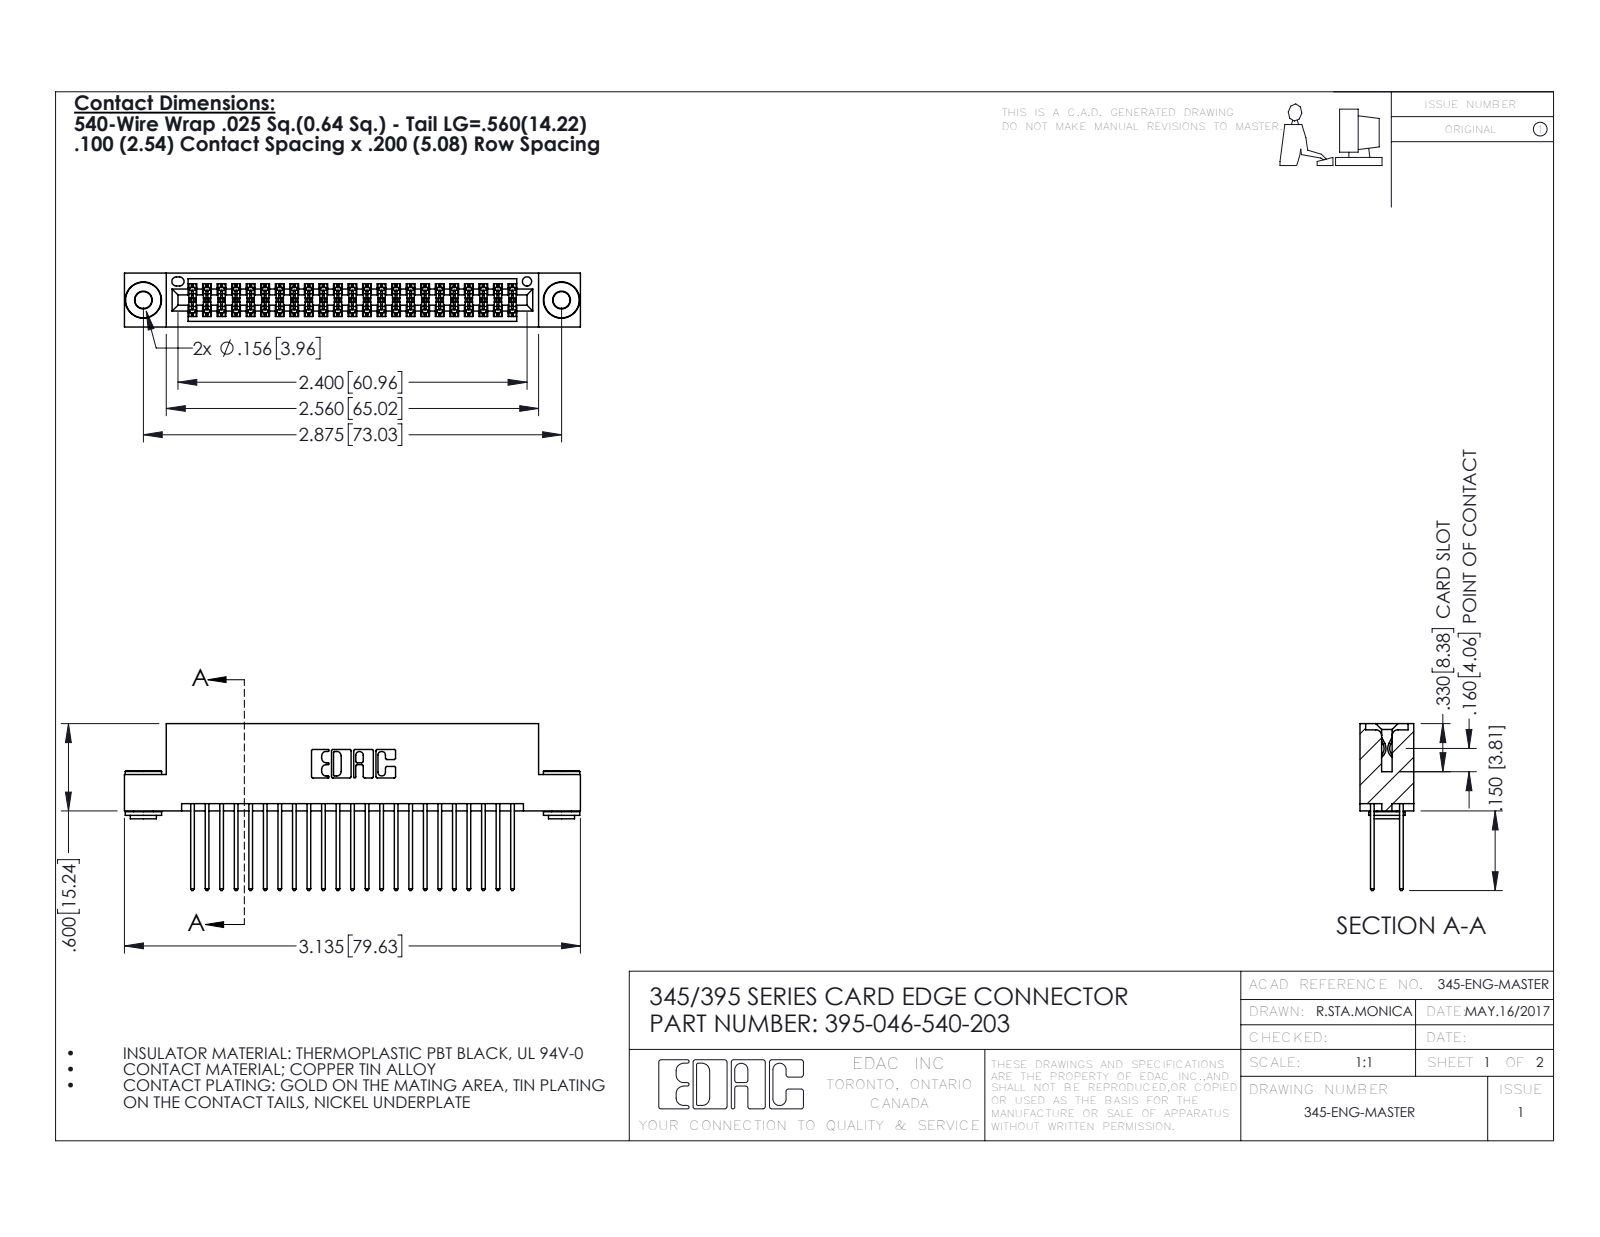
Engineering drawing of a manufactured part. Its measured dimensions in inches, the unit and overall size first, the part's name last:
Units: inches
Overall size (bounding box): 3.135 × 1.147 × 0.37
Round holes (diameter × count): ⌀0.116 ×2, ⌀0.156 ×2, ⌀0.064 ×1
Round bosses / shafts (diameter × count): ⌀0.25 ×2, ⌀0.18 ×2, ⌀0.136 ×2
Partial cylindrical surfaces — rounded edges, fillets, slot ends (radius × count): R0.006 ×69, R0.01 ×46, R0.01 ×22, R0.007 ×6, R0.031 ×6, R0.026 ×3, R0.014 ×2, R0.019 ×2
Main face-to-face distances: 0.072, 0.298, 0.2, 0.025, 0.098, 0.272, 0.37, 0.225, 0.175, 0.149
Hole centre spacings: 0.27, 2.641, 2.875
Volume: 0.473 in³ · Surface area: 18.76 in²
Bodies: 49 solids, 2464 faces (1608 planar, 848 cylindrical, 8 other)
Part name (STEP PRODUCT): 395-046-540-203; 345-292-001_345-293-140; 345 Part_Flush Mounting Lugs - 0.156 Dia-TH; 345-250-002_345-250-002-102
STEP written by: SolidWorks 2016 (CONFIG_CONTROL_DESIGN)
